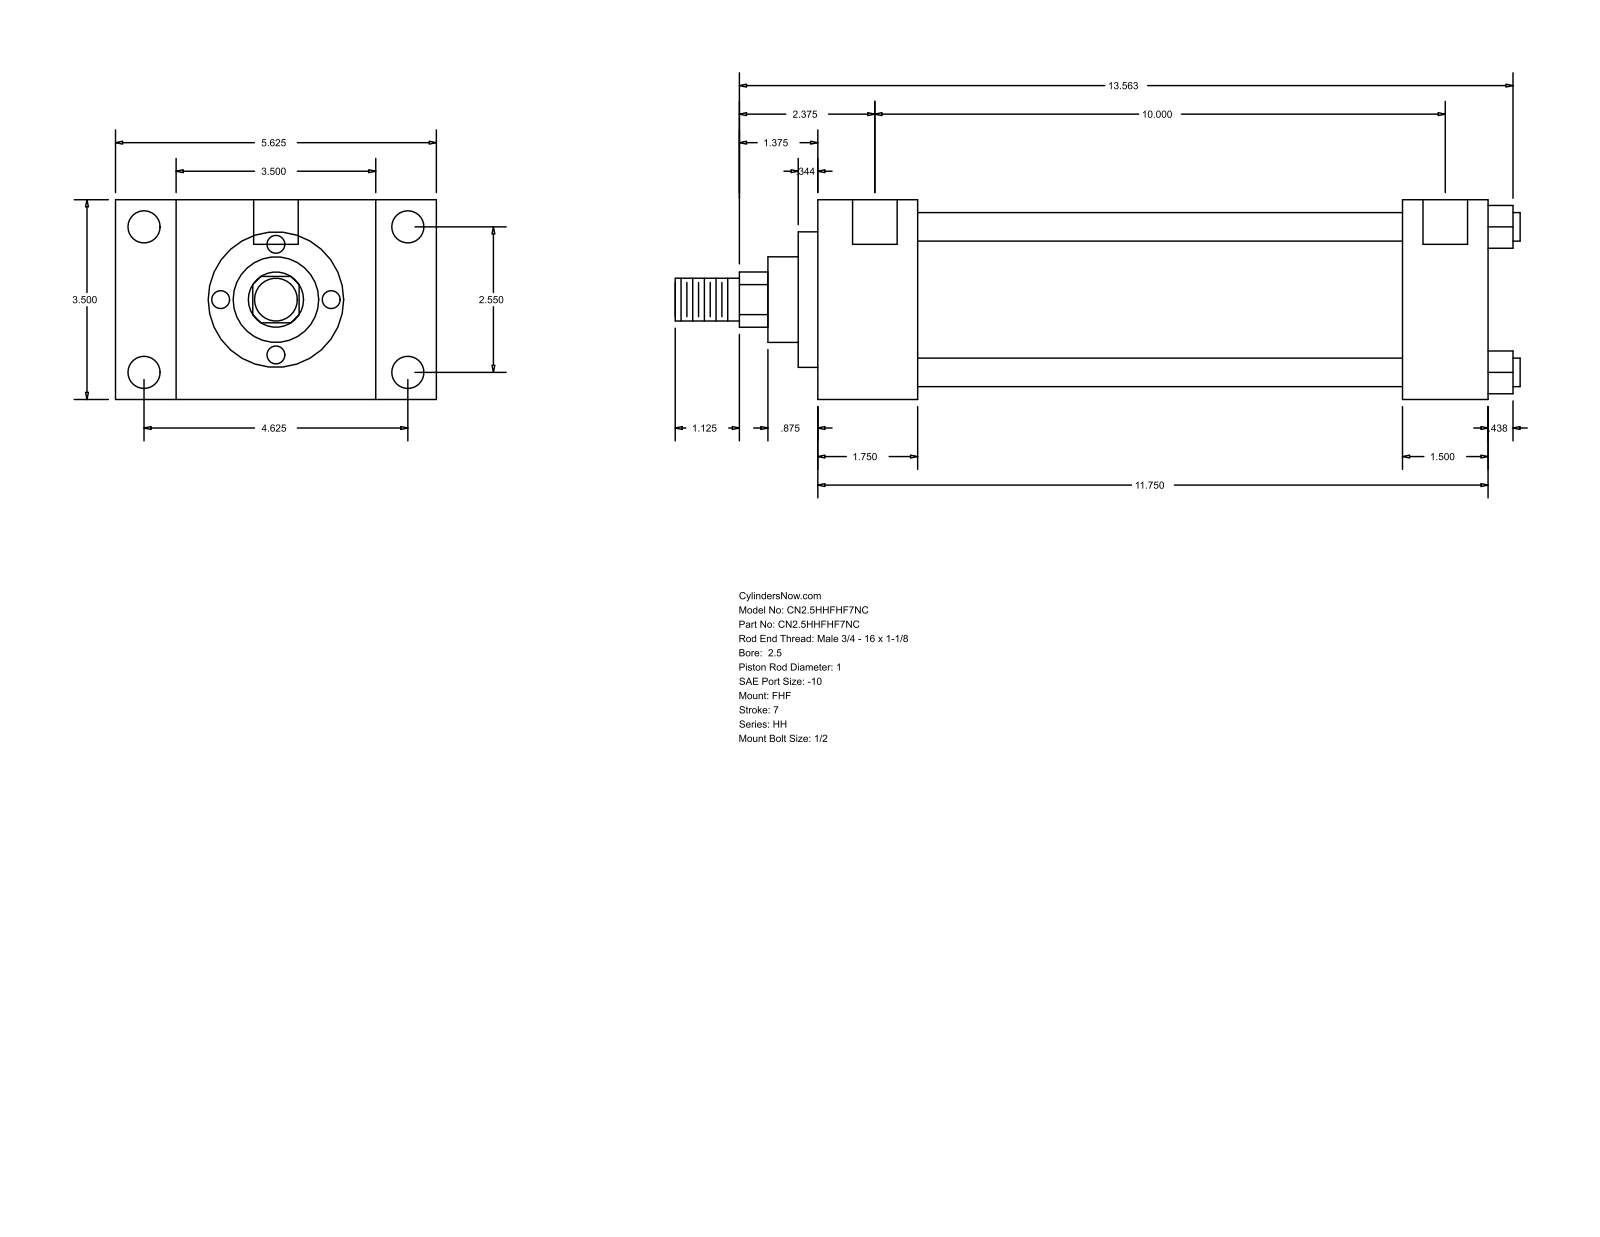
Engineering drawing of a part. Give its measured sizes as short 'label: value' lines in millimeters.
name: HH_FHF__0250_1
written by: GSSL Pune (CONFIG_CONTROL_DESIGN)
unit: mm
bodies: 0 solids, 90 faces (61 planar, 29 cylindrical, 0 other)
size: 376.24 × 142.88 × 88.9
holes: 4× ⌀5.56, 4× ⌀14.3, 2× ⌀19.84
bosses: 4× ⌀12.7, 1× ⌀73.03, 1× ⌀60.33, 1× ⌀38.1, 1× ⌀25.4, 1× ⌀19.05
rounds: 1× R12.29
face distances: 88.9, 44.46, 26.99, 115.89, 298.46, 254, 142.88, 260.35, 215.89, 38.11
hole spacings: 1.59, 64.76, 117.48, 134.15, 255.58, 257.17, 253.99
